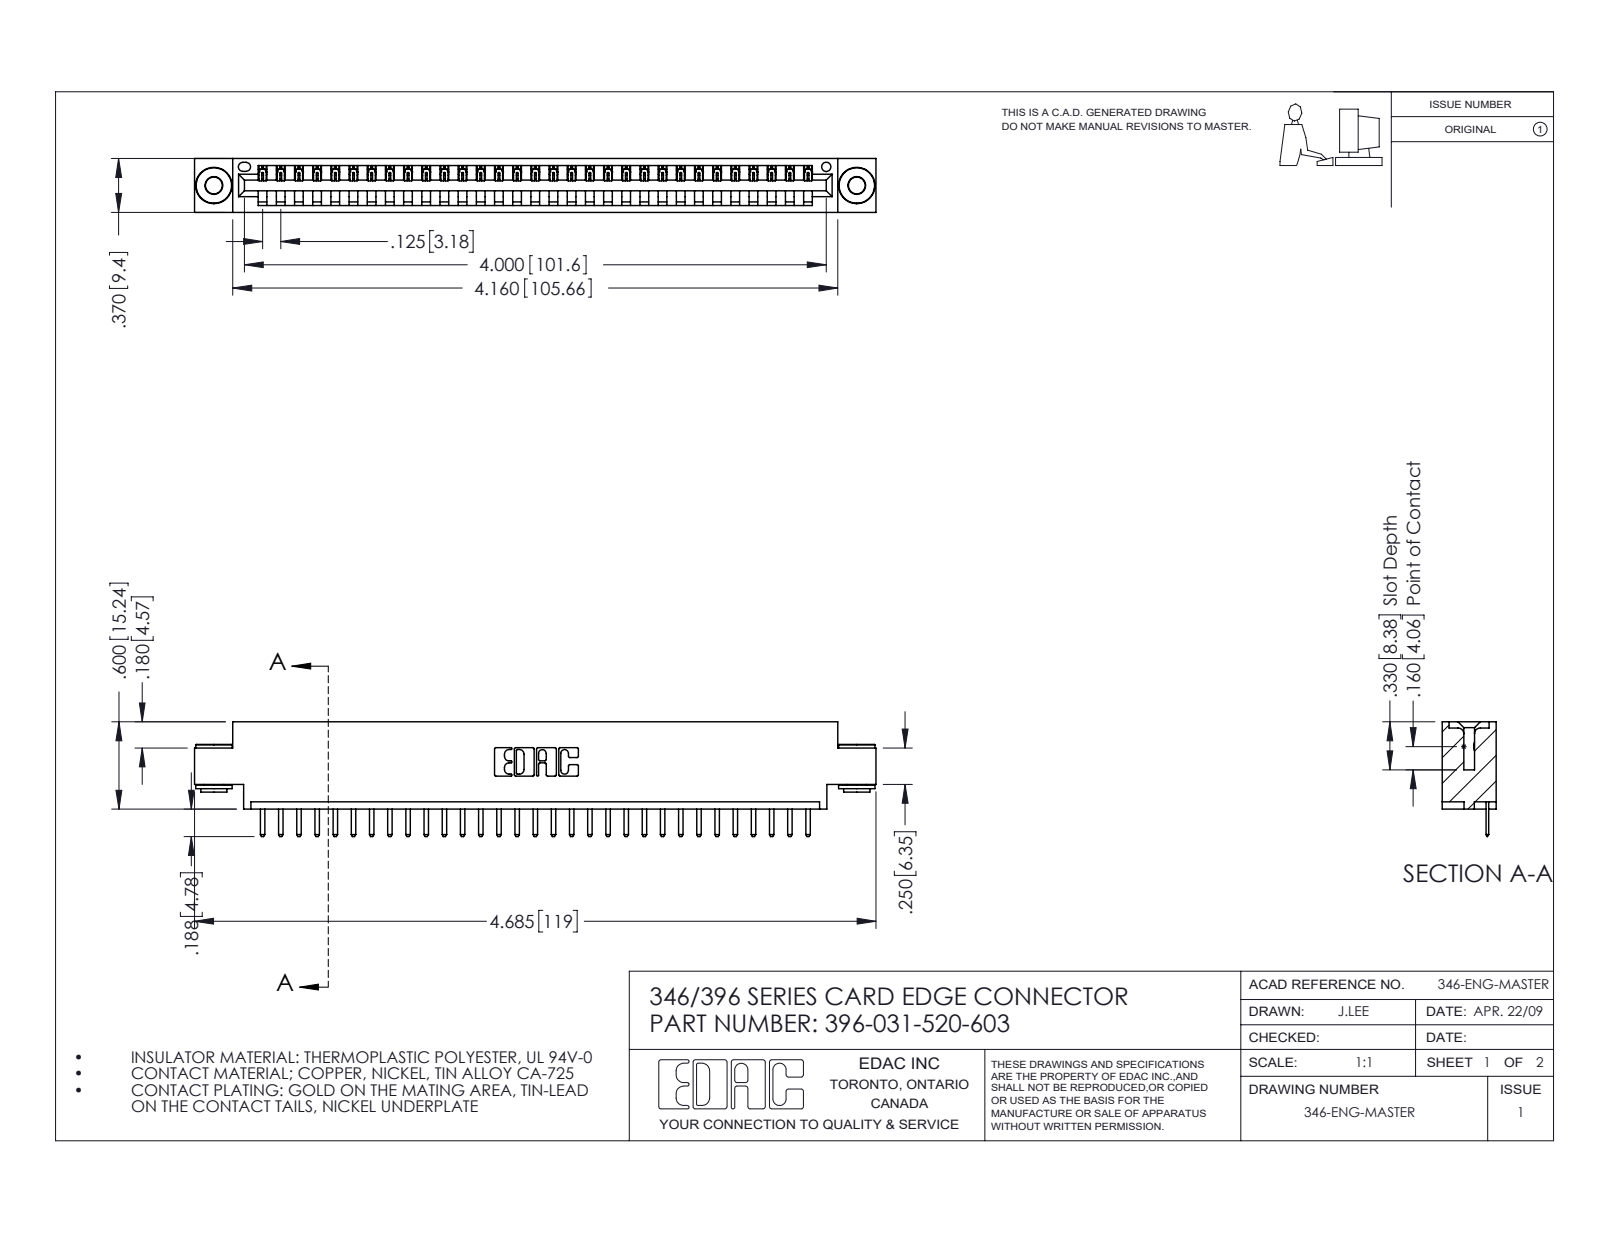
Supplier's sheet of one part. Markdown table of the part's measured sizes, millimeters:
| quantity | value |
| --- | --- |
| part name | 345-292-001_345-293-120; 346 Part_0.170 Offset - 0.156 Dia-TH; 345-250-002_345-250-002-102; 396-031-520-603 |
| STEP written by | SolidWorks 2016 (CONFIG_CONTROL_DESIGN) |
| units | millimeters |
| bodies | 34 solids, 2086 faces (1392 planar, 686 cylindrical, 8 other) |
| overall size | 119 × 20 × 9.4 |
| volume | 11 100 mm³ |
| surface area | 13 830 mm² |
| round holes (diameter × count) | 2.9 × 2, 4 × 2, 1.6 × 1 |
| round bosses / shafts (diameter × count) | 6.4 × 2, 4.6 × 2, 3.5 × 2 |
| partial cylindrical surfaces (radius × count) | 0.3 × 64, 0.2 × 62, 0.3 × 22, 0.2 × 6, 0.8 × 6, 0.7 × 3, 0.8 × 2, 1 × 2 |
| main face-to-face distances | 1.2, 8.2, 9.4, 6.4, 0.6, 3.8, 5.6, 2.5, 4.4, 1.8 |
| hole center spacings | 6.2, 107, 112.3 |
